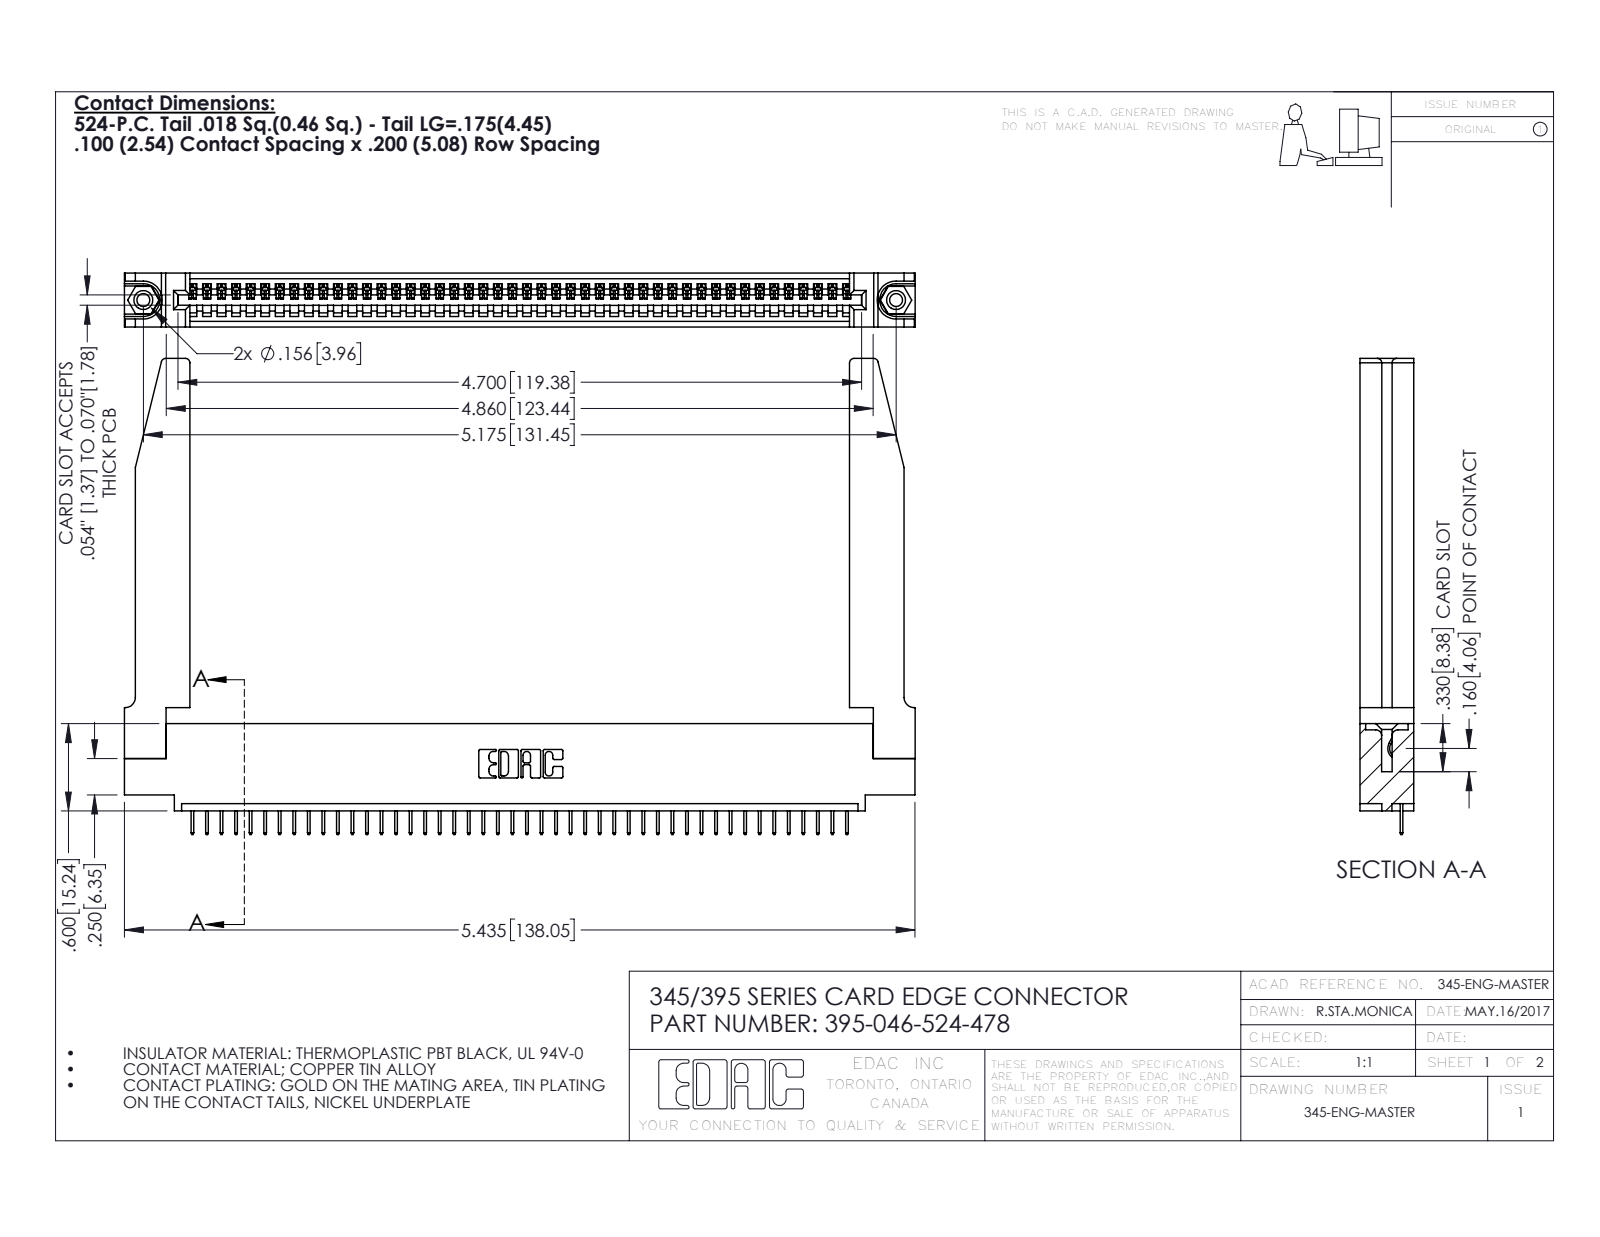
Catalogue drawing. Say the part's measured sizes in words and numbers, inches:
The part is named "395-046-524-478; 345-292-001_345-293-124; 345-220-078_345-220-078; 345-250-001_345-250-001-102 (+1 more)". Its 3-D file was written by "SolidWorks 2016 (CONFIG_CONTROL_DESIGN)". It is 51 solids with 3216 faces: 2342 planar, 822 cylindrical and 52 other. Overall it measures 5.436 by 3.272 by 0.37 inches. Its volume is 1.261 cubic inches and its surface area 36.48 square inches. Round holes: 2 of diameter 0.089, 2 of diameter 0.125, 2 of diameter 0.156, 1 of diameter 0.064. Round bosses or shafts: 2 of diameter 0.155. Partial cylindrical surfaces (rounded edges, fillets, slot ends): 92 of radius 0.006, 22 of radius 0.01, 8 of radius 0.03, 6 of radius 0.007, 6 of radius 0.031, 3 of radius 0.026, 2 of radius 0.031, 2 of radius 0.04. The main face-to-face distances are 0.37, 0.072, 0.298, 0.2, 0.098, 0.272, 0.025, 0.225, 0.148, 0.15. The hole center spacings are 0.27, 4.939, 5.175.
